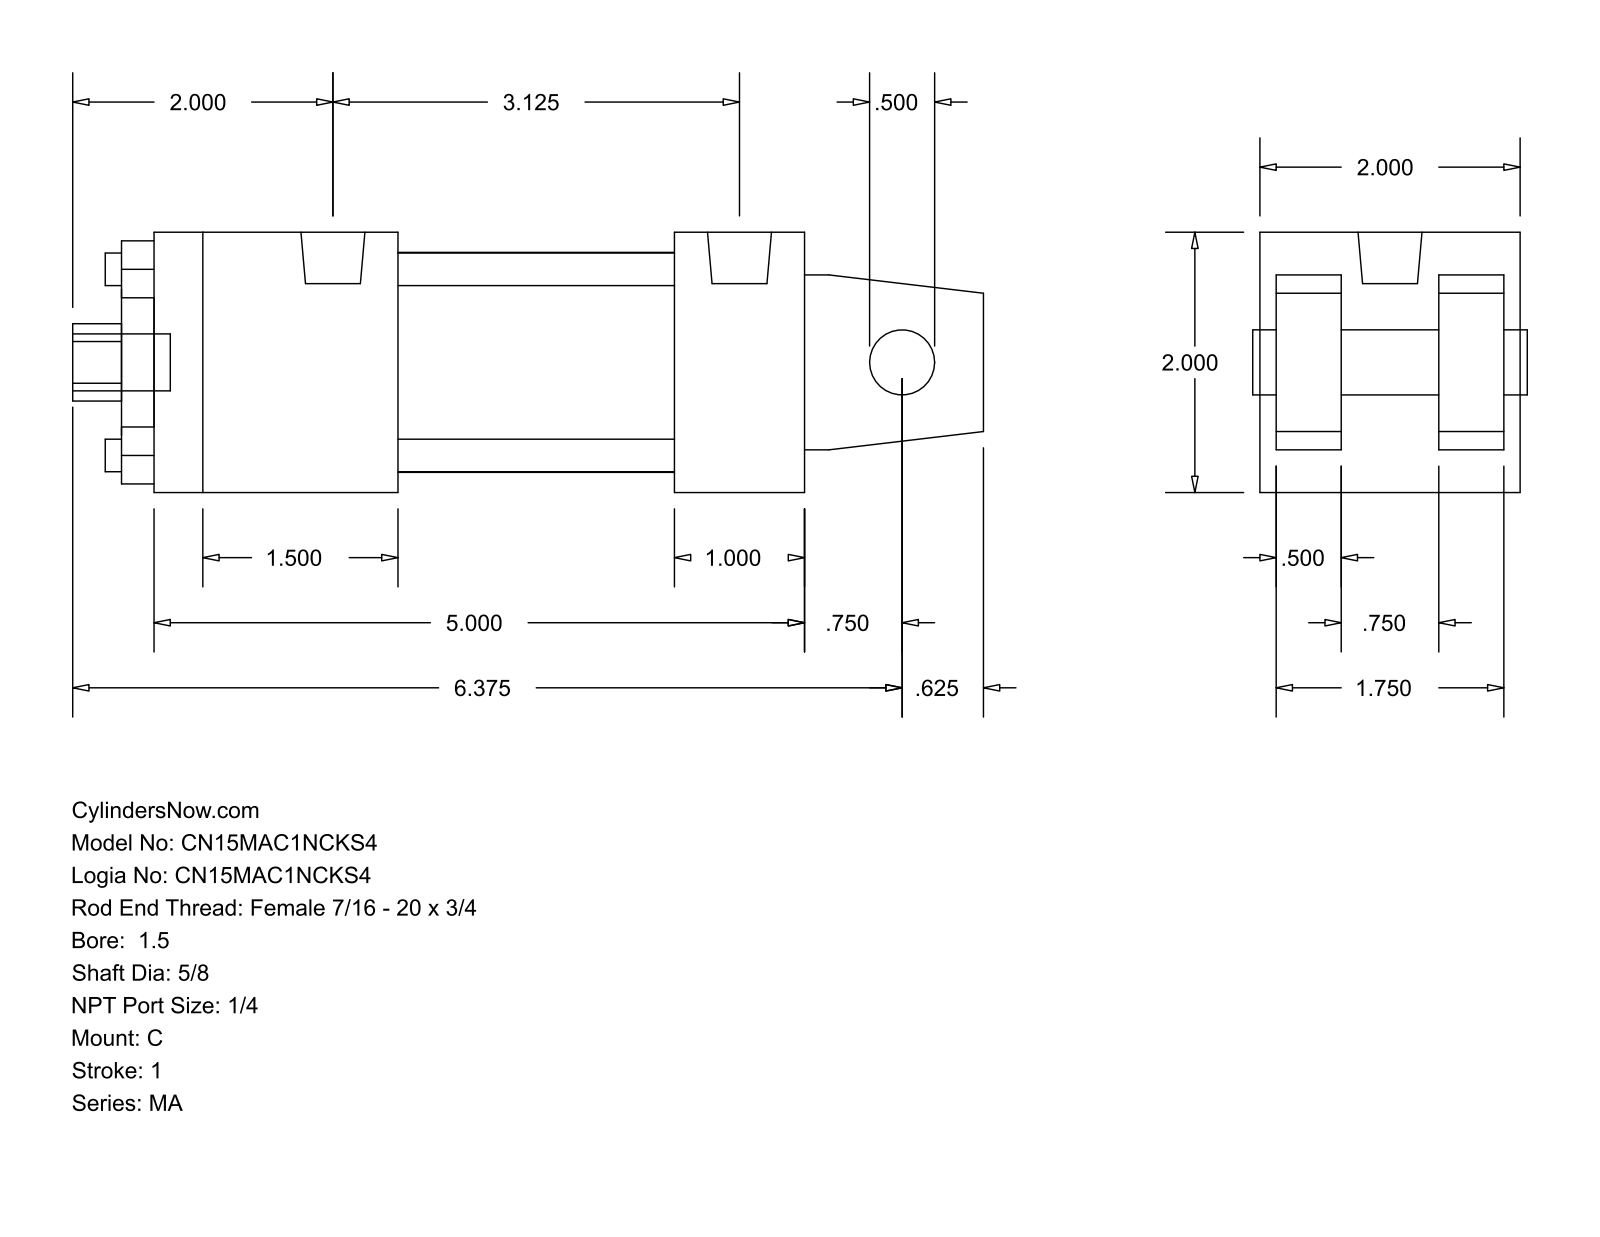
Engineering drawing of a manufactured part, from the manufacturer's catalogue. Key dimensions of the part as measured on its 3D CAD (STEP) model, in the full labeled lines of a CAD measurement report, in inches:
Part name (STEP PRODUCT): MA_C__0150_0.625
STEP written by: GSSL Pune (CONFIG_CONTROL_DESIGN)
Units: inches
Bodies: 0 solids, 103 faces (76 planar, 27 cylindrical, 0 other)
Overall size (bounding box): 7 × 2 × 2
Round holes (diameter × count): ⌀0.25 ×4, ⌀0.5 ×1, ⌀0.625 ×1, ⌀1.125 ×1, ⌀1.69 ×1
Round bosses / shafts (diameter × count): ⌀0.313 ×4, ⌀0.492 ×2, ⌀0.437 ×1
Partial cylindrical surfaces — rounded edges, fillets, slot ends (radius × count): R0.297 ×1
Main face-to-face distances: 2, 0.5, 0.125, 0.625, 1.375, 1.875, 1.25, 2.125, 5, 4
Hole centre spacings: 1.011, 1.43, 2.022
